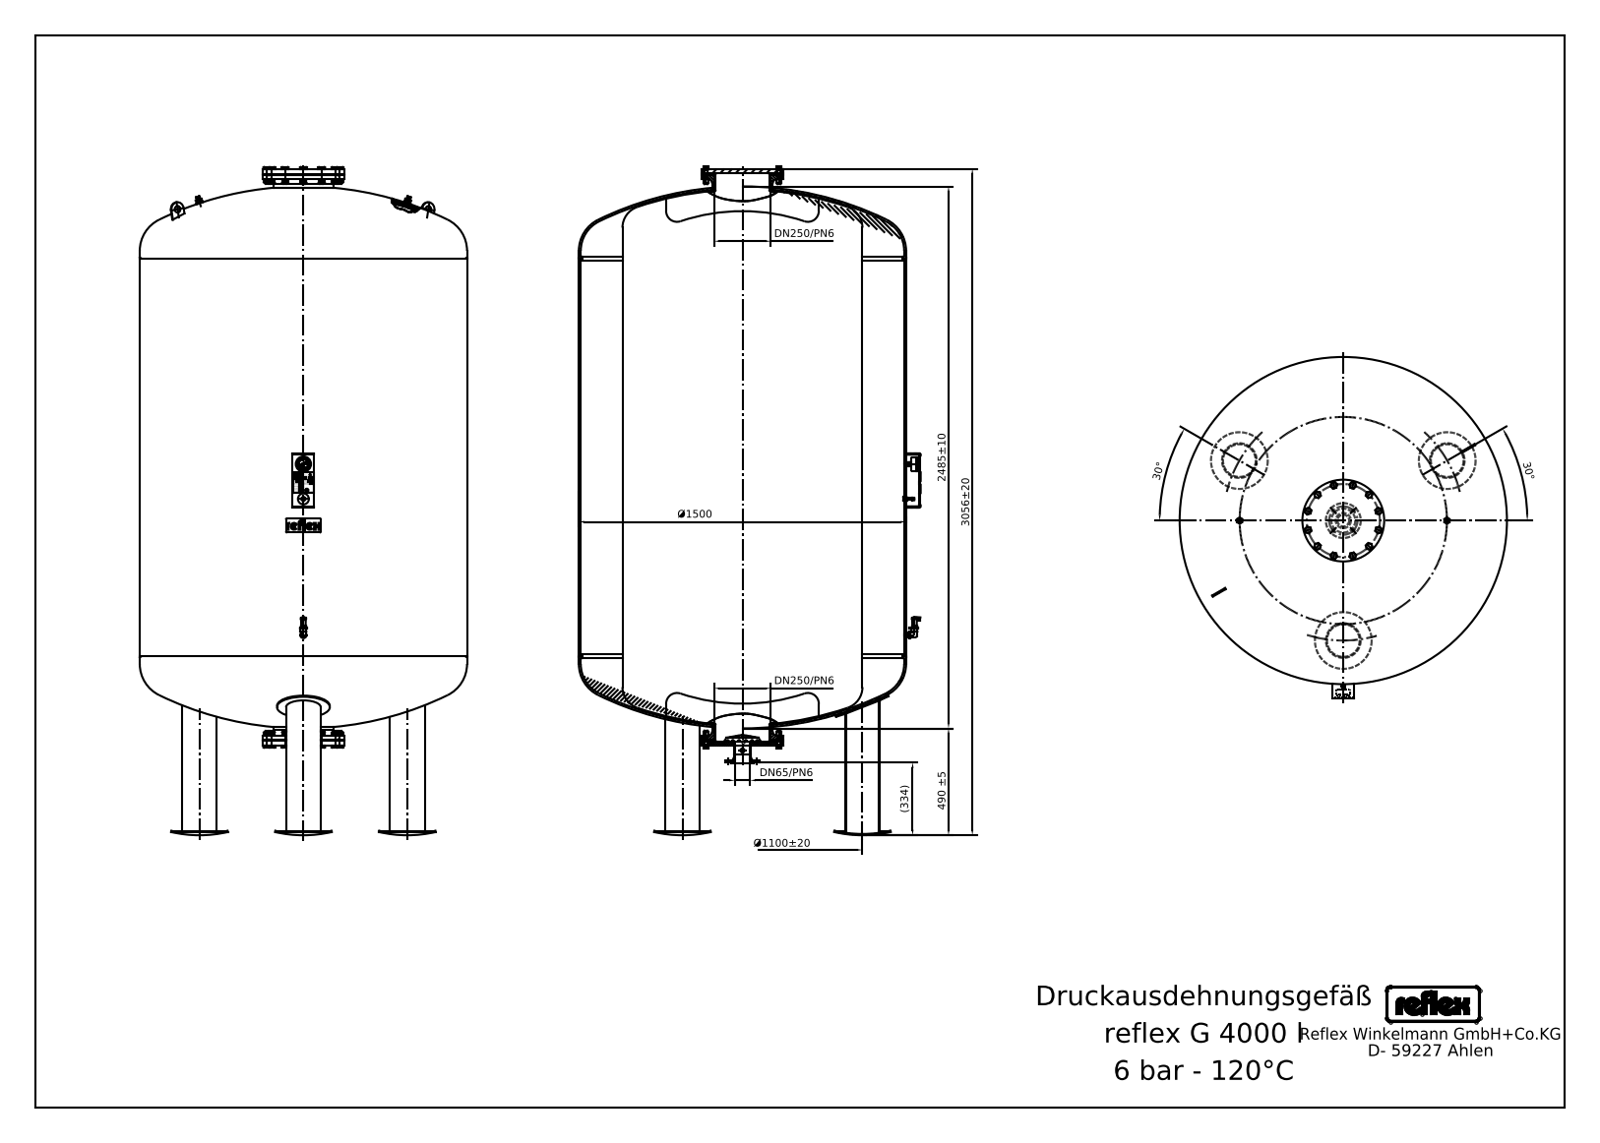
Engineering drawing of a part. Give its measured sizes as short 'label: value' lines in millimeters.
written by: Mechanical Desktop 2008 (CONFIG_CONTROL_DESIGN)
unit: mm
bodies: 20 solids, 800 faces (473 planar, 190 cylindrical, 137 other)
size: 3065 × 1566 × 1502.44
volume: 4 078 000 000 mm³; area: 23 060 000 mm²
holes: 1× ⌀10, 1× ⌀30, 1× ⌀50, 1× ⌀69, 1× ⌀260.4
bosses: 12× ⌀16, 3× ⌀159, 2× ⌀28, 2× ⌀26, 2× ⌀20, 1× ⌀1500, 1× ⌀375, 1× ⌀273
rounds: 4× R8.44, 3× R3.38, 2× R1, 2× R5, 2× R5.76, 2× R10, 2× R10.12, 2× R13.91
face distances: 1825, 22, 2620, 27, 2593, 384, 2214, 389, 2236, 411
hole spacings: 82.33, 765.5
